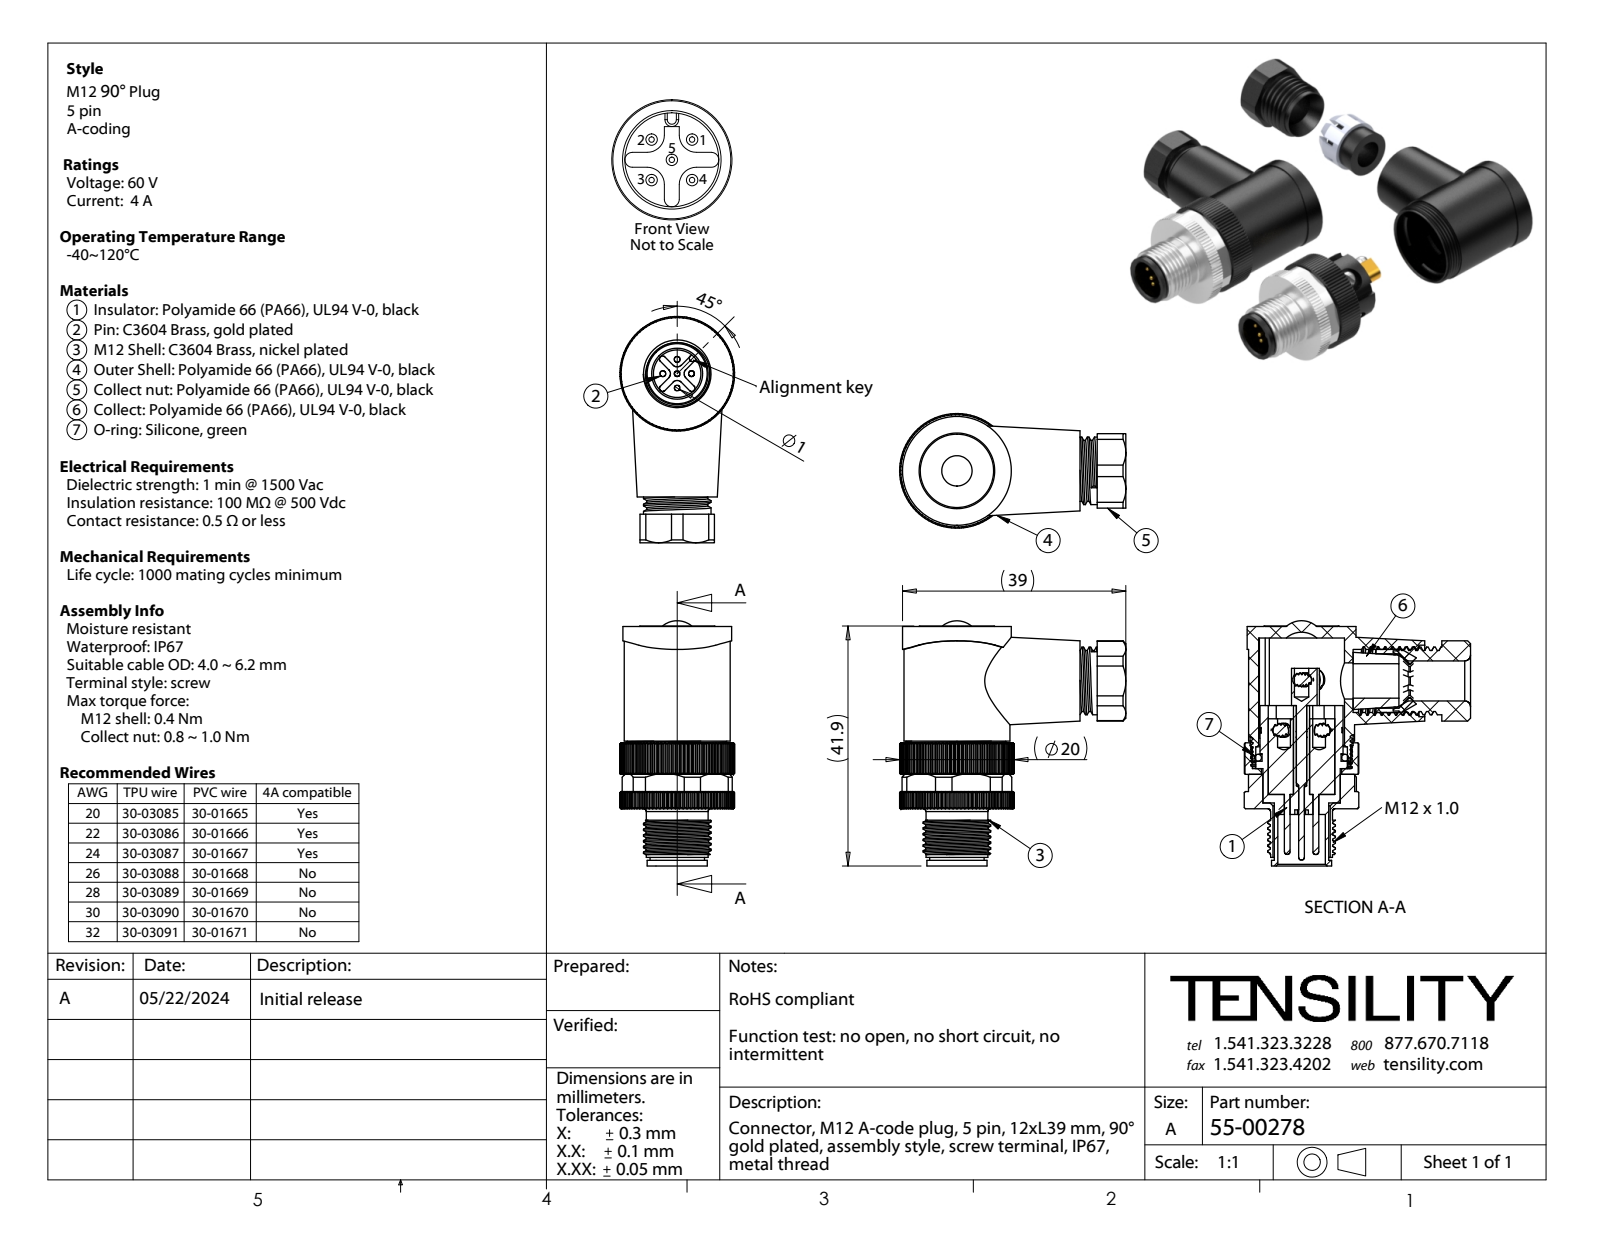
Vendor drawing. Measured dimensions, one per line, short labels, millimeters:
name: 55-00278-11; 55-00278-08; 55-00278-10; 55-00278-07 (+8 more)
written by: SolidWorks 2021 (CONFIG_CONTROL_DESIGN)
unit: mm
bodies: 18 solids, 1652 faces (576 planar, 540 cylindrical, 536 other)
size: 75.34 × 71.87 × 20
volume: 9 129 mm³; area: 14 250 mm²
holes: 9× ⌀2.5, 5× ⌀1, 5× ⌀2.05, 4× ⌀5, 1× ⌀6, 1× ⌀6.3, 1× ⌀7, 1× ⌀8.3, 1× ⌀9.5, 1× ⌀10, 1× ⌀11, 1× ⌀12.5
bosses: 5× ⌀3.5, 5× ⌀2.4, 2× ⌀11.8, 2× ⌀10.5, 1× ⌀20, 1× ⌀19, 1× ⌀18.5, 1× ⌀17.8
rounds: 5× R0.55, 5× R1.75, 4× R1, 1× R6.45, 1× R6.5, 1× R7, 1× R9.65
face distances: 1, 6, 54.87, 2, 13.86, 60.87, 7, 18, 5, 4.5
hole spacings: 5.14, 5.13, 0.8, 2.5, 3.12, 3.54, 3.62, 4.34
